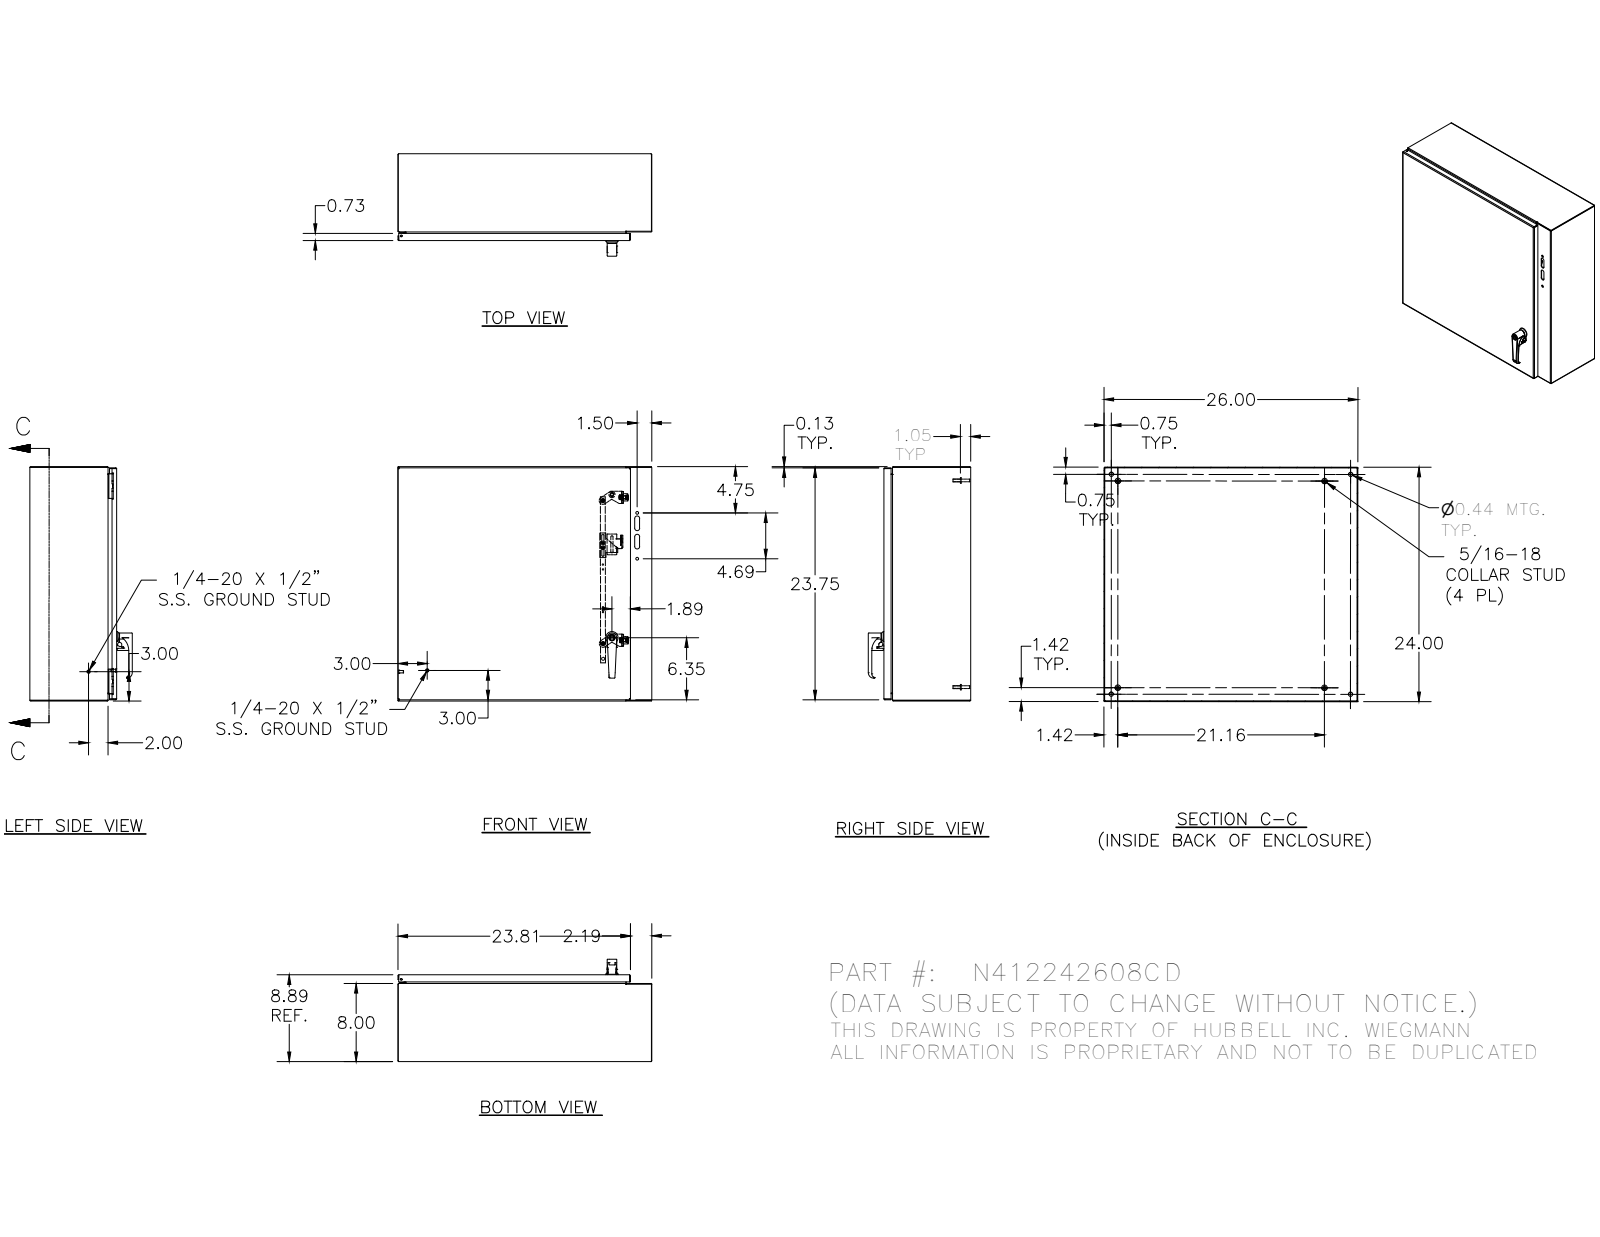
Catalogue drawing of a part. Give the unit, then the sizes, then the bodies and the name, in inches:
Units: inches
Overall size (bounding box): 26 × 24 × 10.512
Round holes (diameter × count): ⌀0.145 ×6, ⌀0.093 ×4, ⌀0.152 ×4, ⌀0.156 ×4, ⌀0.167 ×4, ⌀0.172 ×4, ⌀0.187 ×4, ⌀0.437 ×4, ⌀0.32 ×3, ⌀0.196 ×2, ⌀0.211 ×2, ⌀0.22 ×2
Round bosses / shafts (diameter × count): ⌀0.25 ×12, ⌀0.3 ×8, ⌀0.563 ×4, ⌀0.437 ×4, ⌀0.36 ×4, ⌀0.32 ×4, ⌀0.275 ×4, ⌀0.256 ×4
Partial cylindrical surfaces — rounded edges, fillets, slot ends (radius × count): R0.02 ×38, R0.012 ×30, R0.05 ×26, R0.125 ×25, R0.016 ×18, R0.016 ×16, R0.025 ×16, R0.09 ×16
Main face-to-face distances: 0.074, 8.843, 8.769, 8.917, 23.926, 25.926, 0.917, 7.926, 24, 23.852
Hole centre spacings: 20, 0.5, 24.9, 0.656, 0.66, 0.984, 1.307, 1.311
Volume: 171.3 in³ · Surface area: 4 588 in²
Bodies: 60 solids, 2072 faces (812 planar, 742 cylindrical, 518 other)
Part name (STEP PRODUCT): N412242608CD
STEP written by: SolidWorks 2019 (AUTOMOTIVE_DESIGN)
